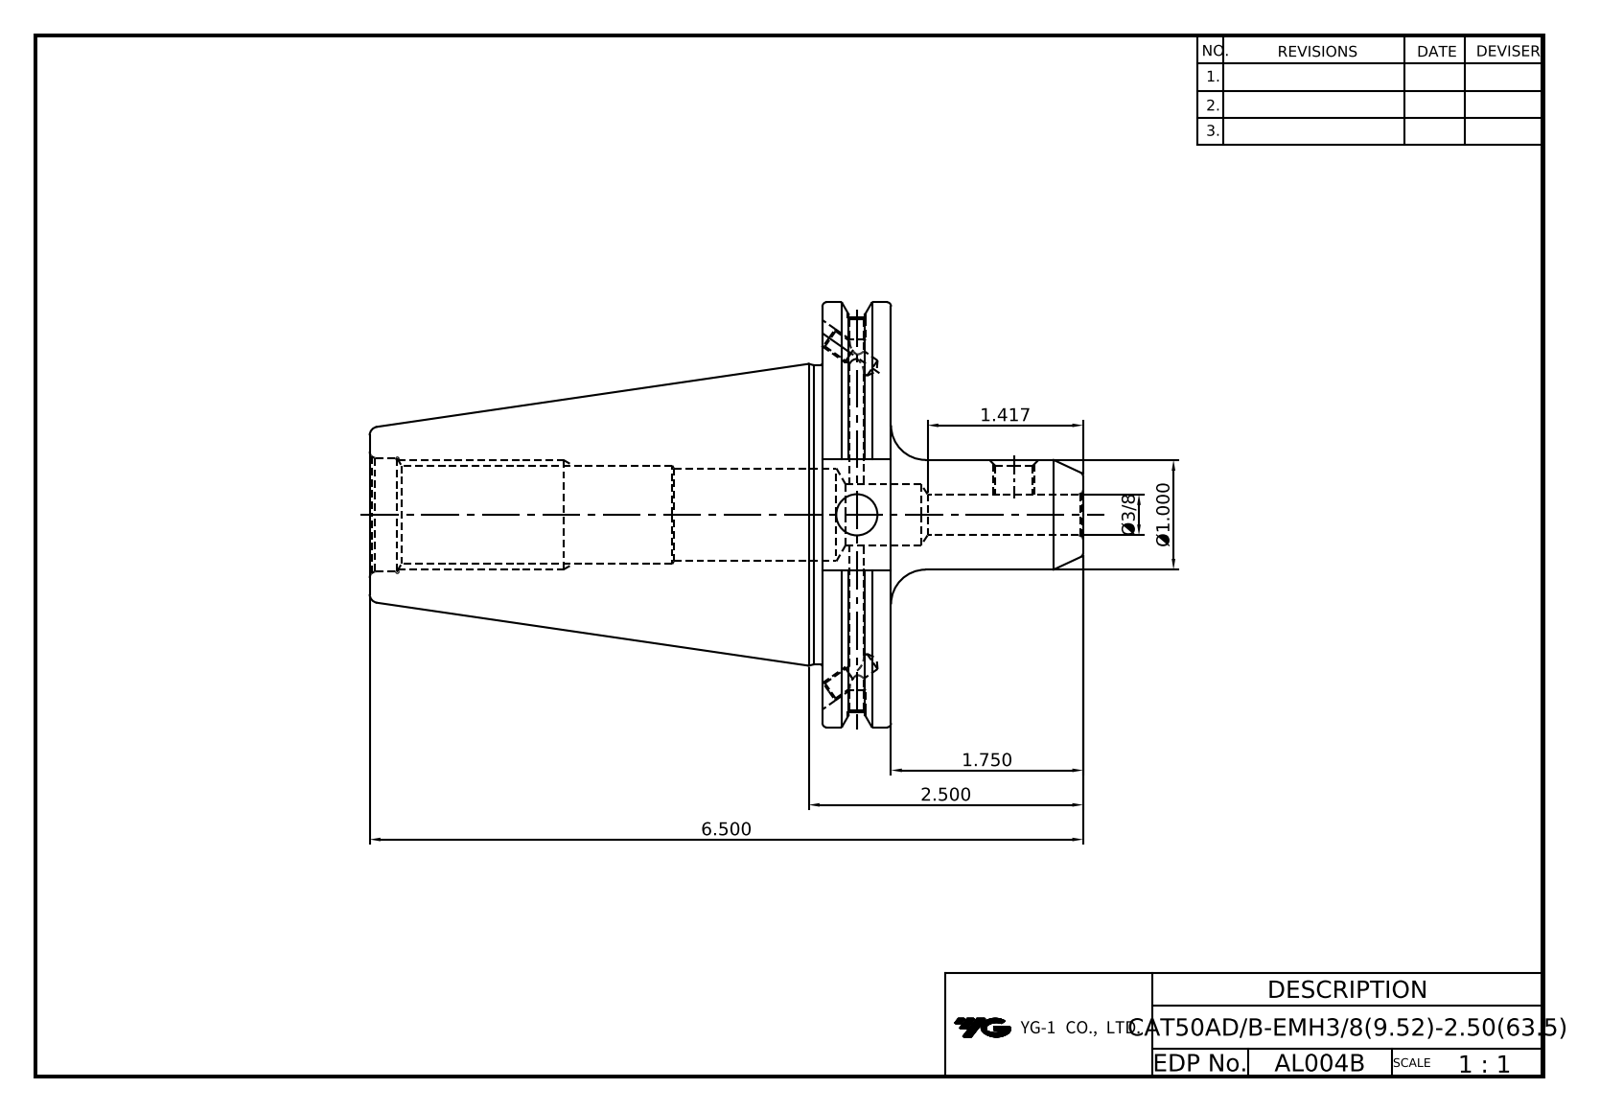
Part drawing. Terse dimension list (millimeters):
name: LO-CAT50ADB-EMH9.525-2.50
written by: Autodesk Inventor 2024 (AUTOMOTIVE_DESIGN)
unit: mm
bodies: 1 solid, 86 faces (35 planar, 27 cylindrical, 24 other)
size: 165.1 × 98.42 × 94.69
volume: 340 474 mm³; area: 49 431 mm²
holes: 2× ⌀3.24, 2× ⌀4.13, 2× ⌀4.2, 2× ⌀5, 1× ⌀8.38, 1× ⌀9.52, 1× ⌀9.53, 1× ⌀14, 1× ⌀21.5, 1× ⌀21.97, 1× ⌀26.2
bosses: 1× ⌀98.42, 1× ⌀91.29, 1× ⌀69.25, 1× ⌀25.4
face distances: 15.88, 104.77, 120.65, 73.03, 25.9, 110.82, 6.05, 9.83, 114.65, 9.88
